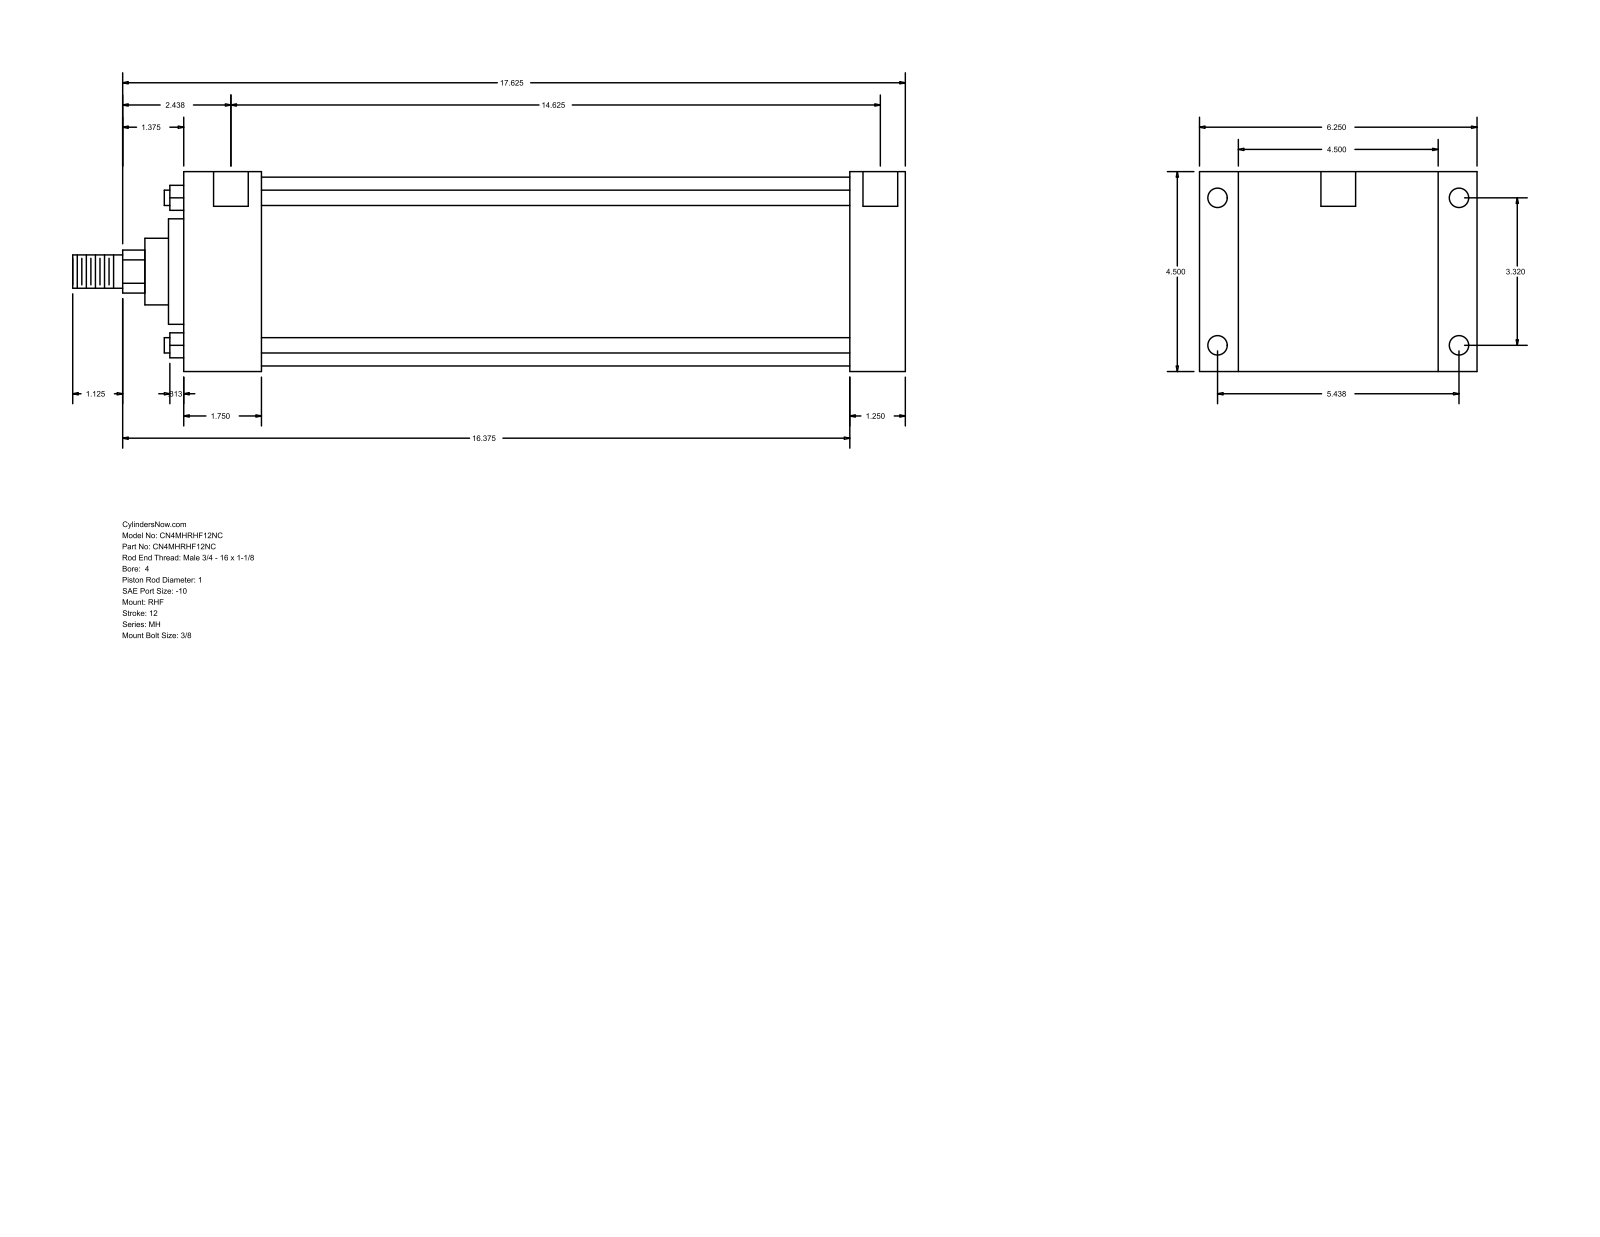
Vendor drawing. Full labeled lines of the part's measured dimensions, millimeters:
Part name (STEP PRODUCT): MH_RHF__0400_1
STEP written by: GSSL Pune (CONFIG_CONTROL_DESIGN)
Units: millimetres
Bodies: 0 solids, 90 faces (61 planar, 29 cylindrical, 0 other)
Overall size (bounding box): 476.25 × 158.75 × 114.3
Round holes (diameter × count): ⌀8.73 ×4, ⌀11.13 ×4, ⌀19.84 ×2
Round bosses / shafts (diameter × count): ⌀8.76 ×4, ⌀107.95 ×1, ⌀60.33 ×1, ⌀38.1 ×1, ⌀25.4 ×1, ⌀19.05 ×1
Partial cylindrical surfaces — rounded edges, fillets, slot ends (radius × count): R12.29 ×1
Main face-to-face distances: 114.3, 412.76, 381.01, 31.75, 22.23, 136.53, 44.46, 336.55, 368.3, 158.76
Hole centre spacings: 84.32, 138.12, 161.82, 374.65, 1.58, 1.59, 371.48, 373.06
